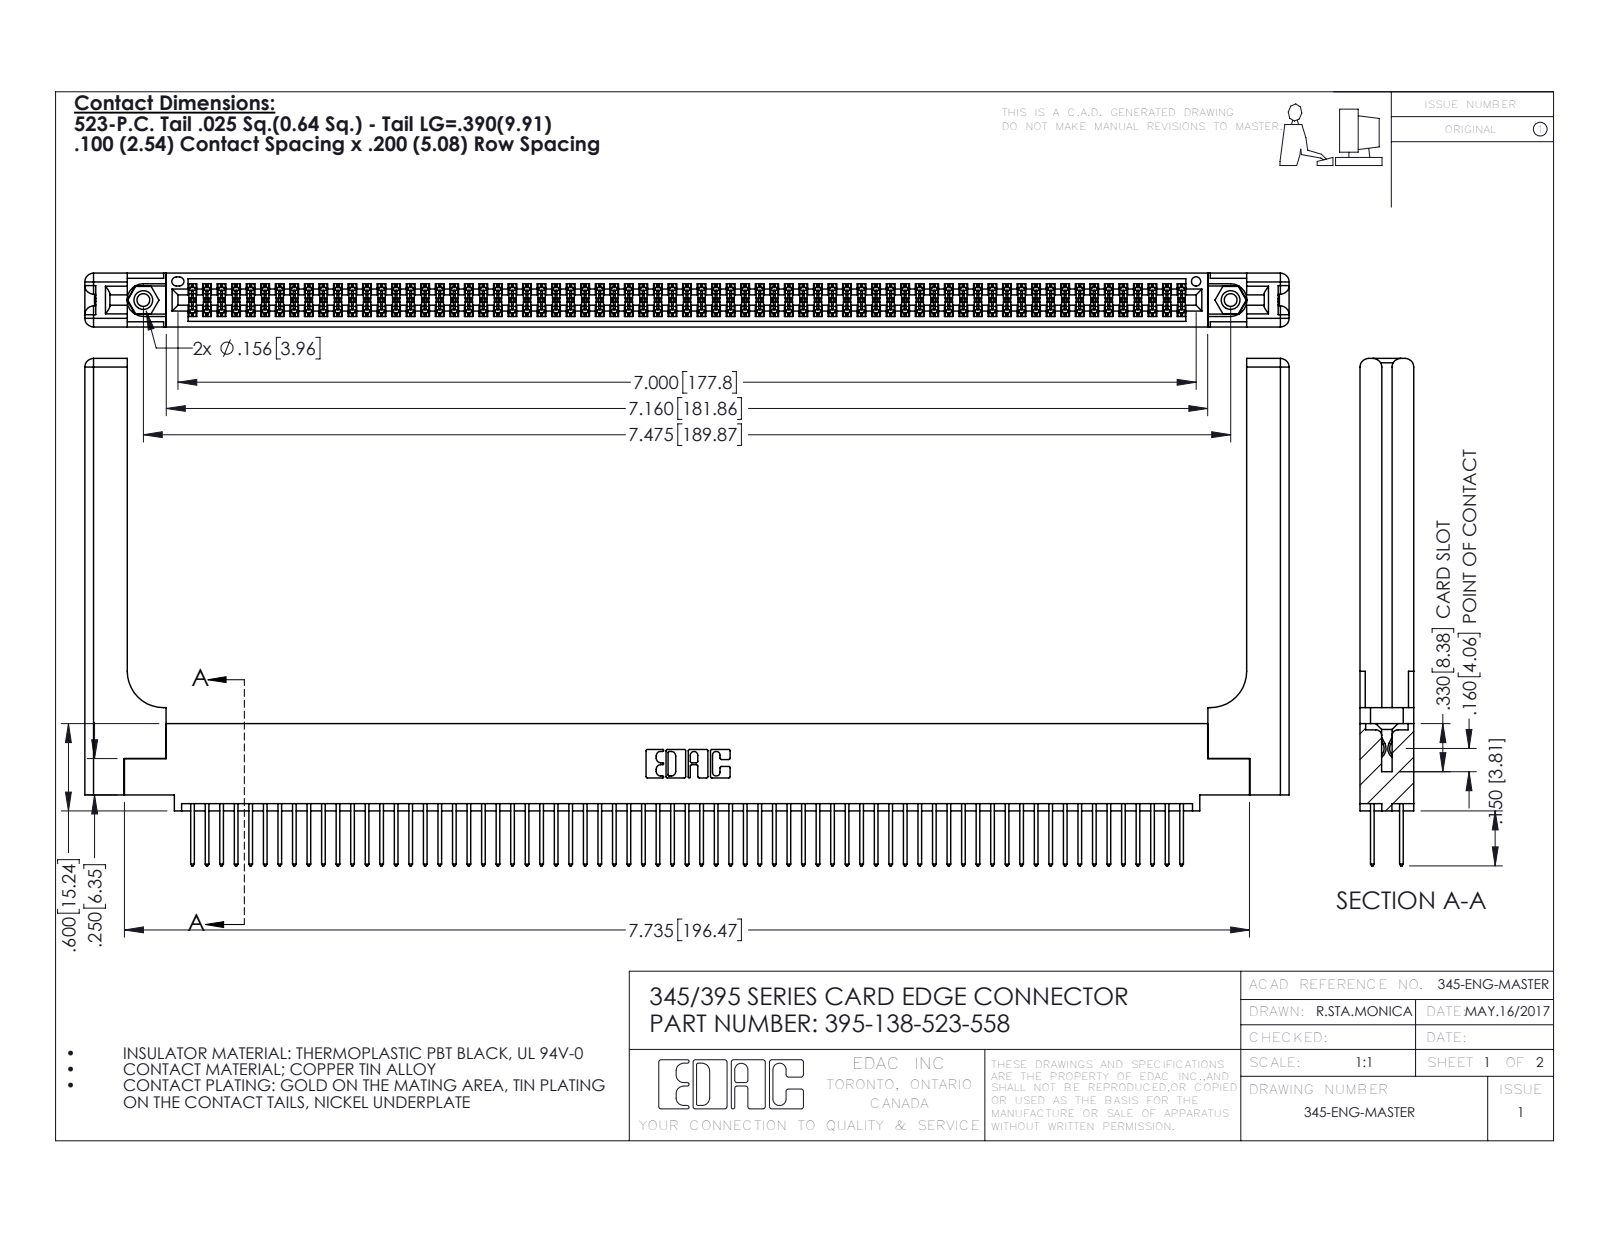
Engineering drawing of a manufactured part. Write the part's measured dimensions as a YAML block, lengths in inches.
part_name: "395-138-523-558; 345-220-058_345-220-058; 345-292-001_345-293-123; 345 Part_0.110 Offset - 0.156 Dia-TH (+1 more)"
step_written_by: "SolidWorks 2016 (CONFIG_CONTROL_DESIGN)"
units: inches
bodies: {solids: 143, faces: 7286, planar: 4786, cylindrical: 2440, other: 60}
overall_size: [8.279, 3.487, 0.37]
volume: 1.792
surface_area: 58.62
round_holes:
  - {diameter: 0.089, count: 2}
  - {diameter: 0.125, count: 2}
  - {diameter: 0.156, count: 2}
  - {diameter: 0.064, count: 1}
round_bosses_or_shafts:
  - {diameter: 0.155, count: 2}
partial_cylinders:
  - {radius: 0.006, count: 207}
  - {radius: 0.01, count: 138}
  - {radius: 0.01, count: 22}
  - {radius: 0.06, count: 16}
  - {radius: 0.007, count: 6}
  - {radius: 0.031, count: 6}
  - {radius: 0.026, count: 3}
  - {radius: 0.014, count: 2}
face_to_face_distances: [0.072, 0.298, 0.37, 0.098, 0.272, 0.025, 0.2, 0.225, 0.175, 0.148]
hole_center_spacings: [0.27, 7.239, 7.475]
